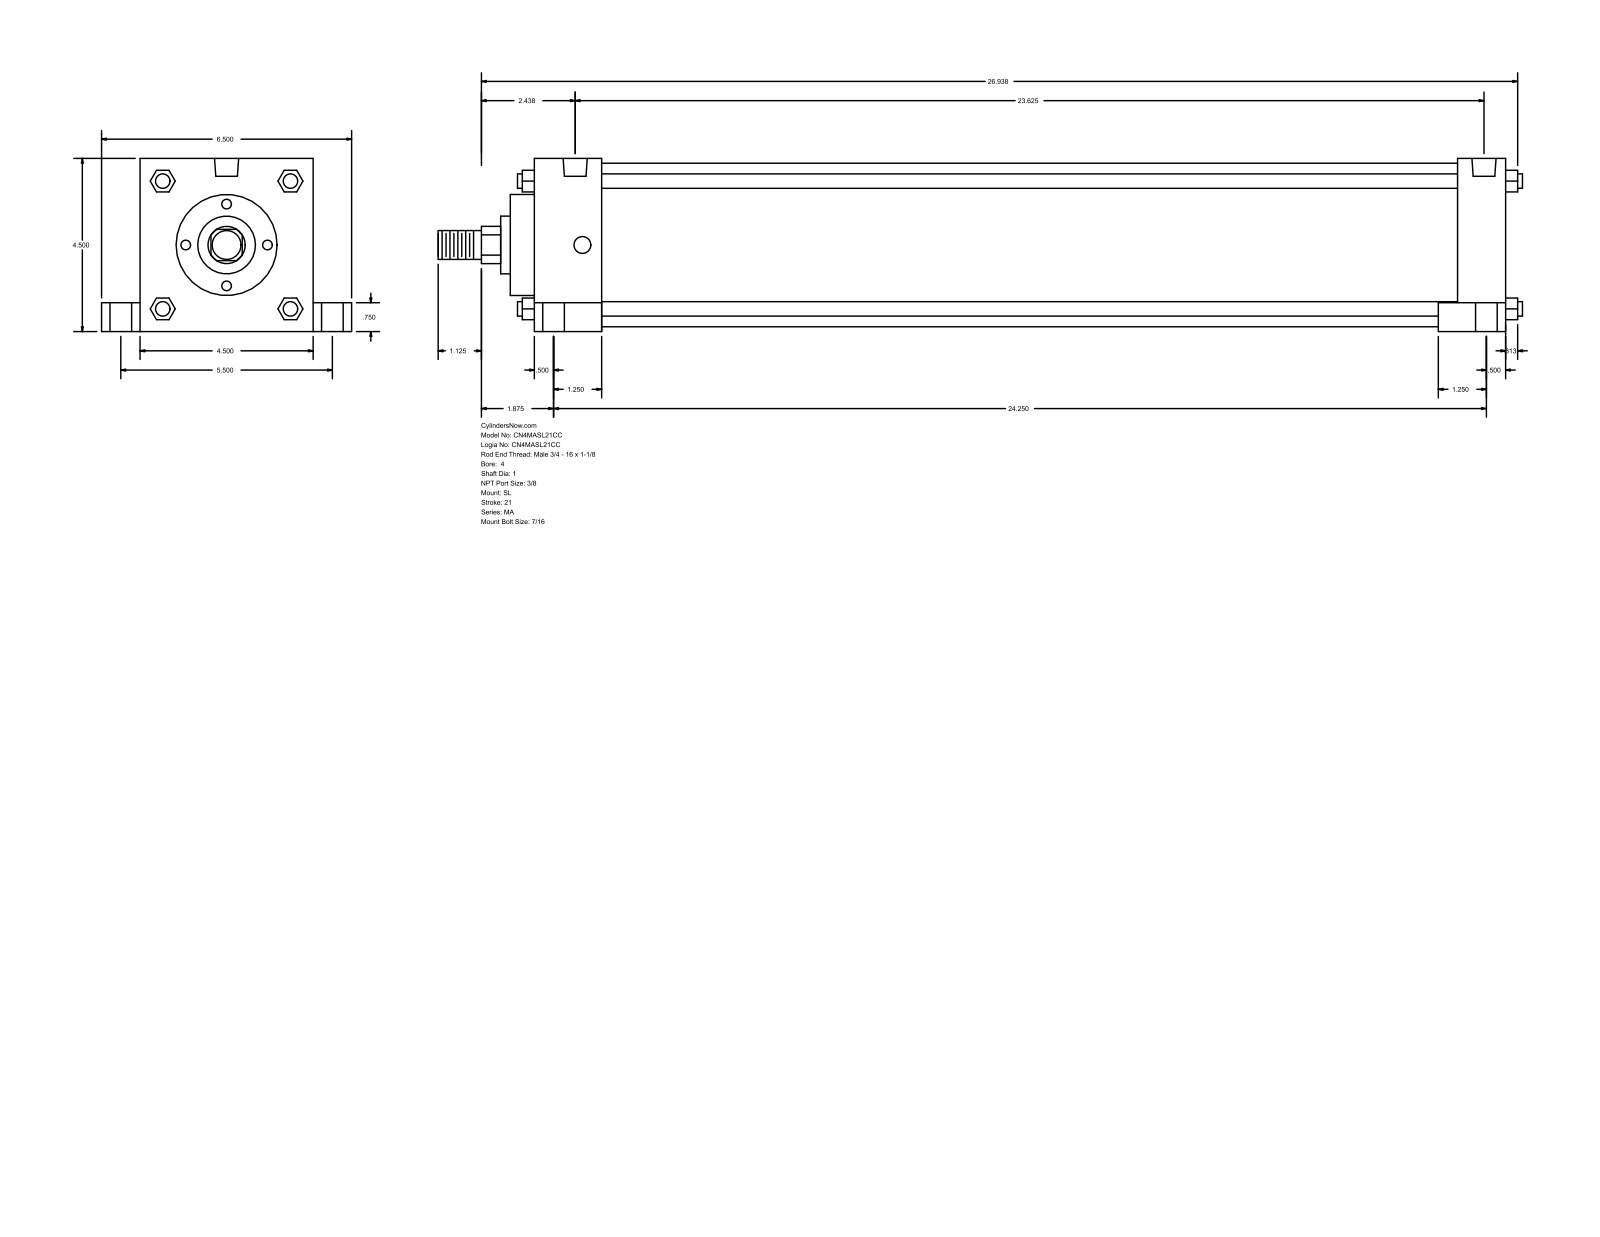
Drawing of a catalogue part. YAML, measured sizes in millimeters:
part_name: "MA_SL__0400_1"
step_written_by: "GSSL Pune (CONFIG_CONTROL_DESIGN)"
units: millimeters
bodies: {solids: 0, faces: 150, planar: 113, cylindrical: 37, other: 0}
overall_size: [715.96, 165.1, 114.3]
round_holes:
  - {diameter: 11.11, count: 4}
  - {diameter: 14.29, count: 4}
  - {diameter: 20.64, count: 4}
  - {diameter: 15.93, count: 2}
round_bosses_or_shafts:
  - {diameter: 9.53, count: 4}
  - {diameter: 107.95, count: 1}
  - {diameter: 66.67, count: 1}
  - {diameter: 38.1, count: 1}
  - {diameter: 25.4, count: 1}
  - {diameter: 19.05, count: 1}
partial_cylinders:
  - {radius: 12.29, count: 1}
face_to_face_distances: [114.3, 641.35, 44.46, 596.89, 609.6, 565.14, 31.75, 25.4, 139.7, 657.22]
hole_center_spacings: [4.76, 69.87, 70.14, 71.3, 72.4, 139.7, 590.56, 595.32]
